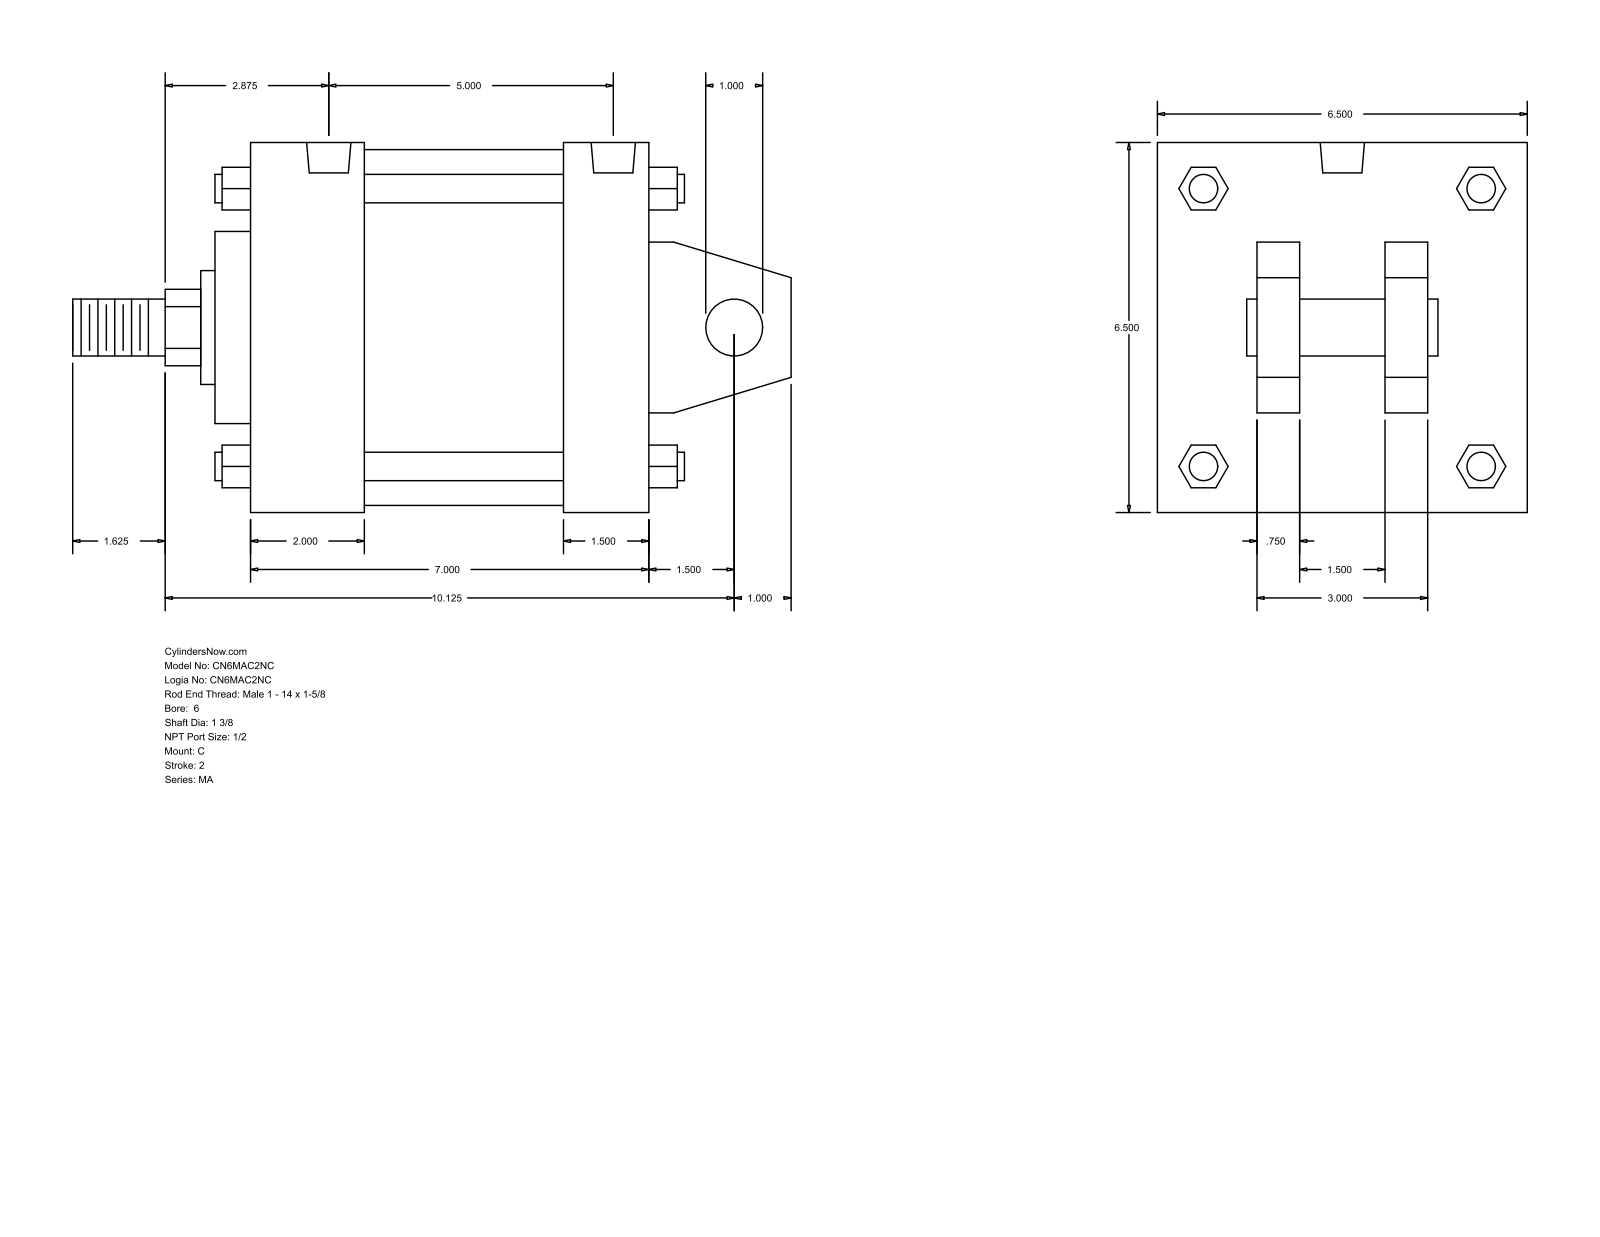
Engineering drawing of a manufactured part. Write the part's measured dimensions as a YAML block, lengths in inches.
part_name: "MA_C__0600_1.375"
step_written_by: "GSSL Pune (CONFIG_CONTROL_DESIGN)"
units: inches
bodies: {solids: 0, faces: 141, planar: 109, cylindrical: 32, other: 0}
overall_size: [12.625, 6.5, 6.5]
round_holes:
  - {diameter: 0.687, count: 4}
  - {diameter: 0.778, count: 2}
round_bosses_or_shafts:
  - {diameter: 0.5, count: 4}
  - {diameter: 1, count: 2}
  - {diameter: 6.25, count: 1}
  - {diameter: 3.375, count: 1}
  - {diameter: 2, count: 1}
  - {diameter: 1.375, count: 1}
partial_cylinders:
  - {radius: 0.672, count: 1}
face_to_face_distances: [6.5, 7, 1.5, 0.75, 2.5, 4, 2, 1.75, 4.75, 5.5]
hole_center_spacings: [5, 0.125, 4.875, 5.125]
